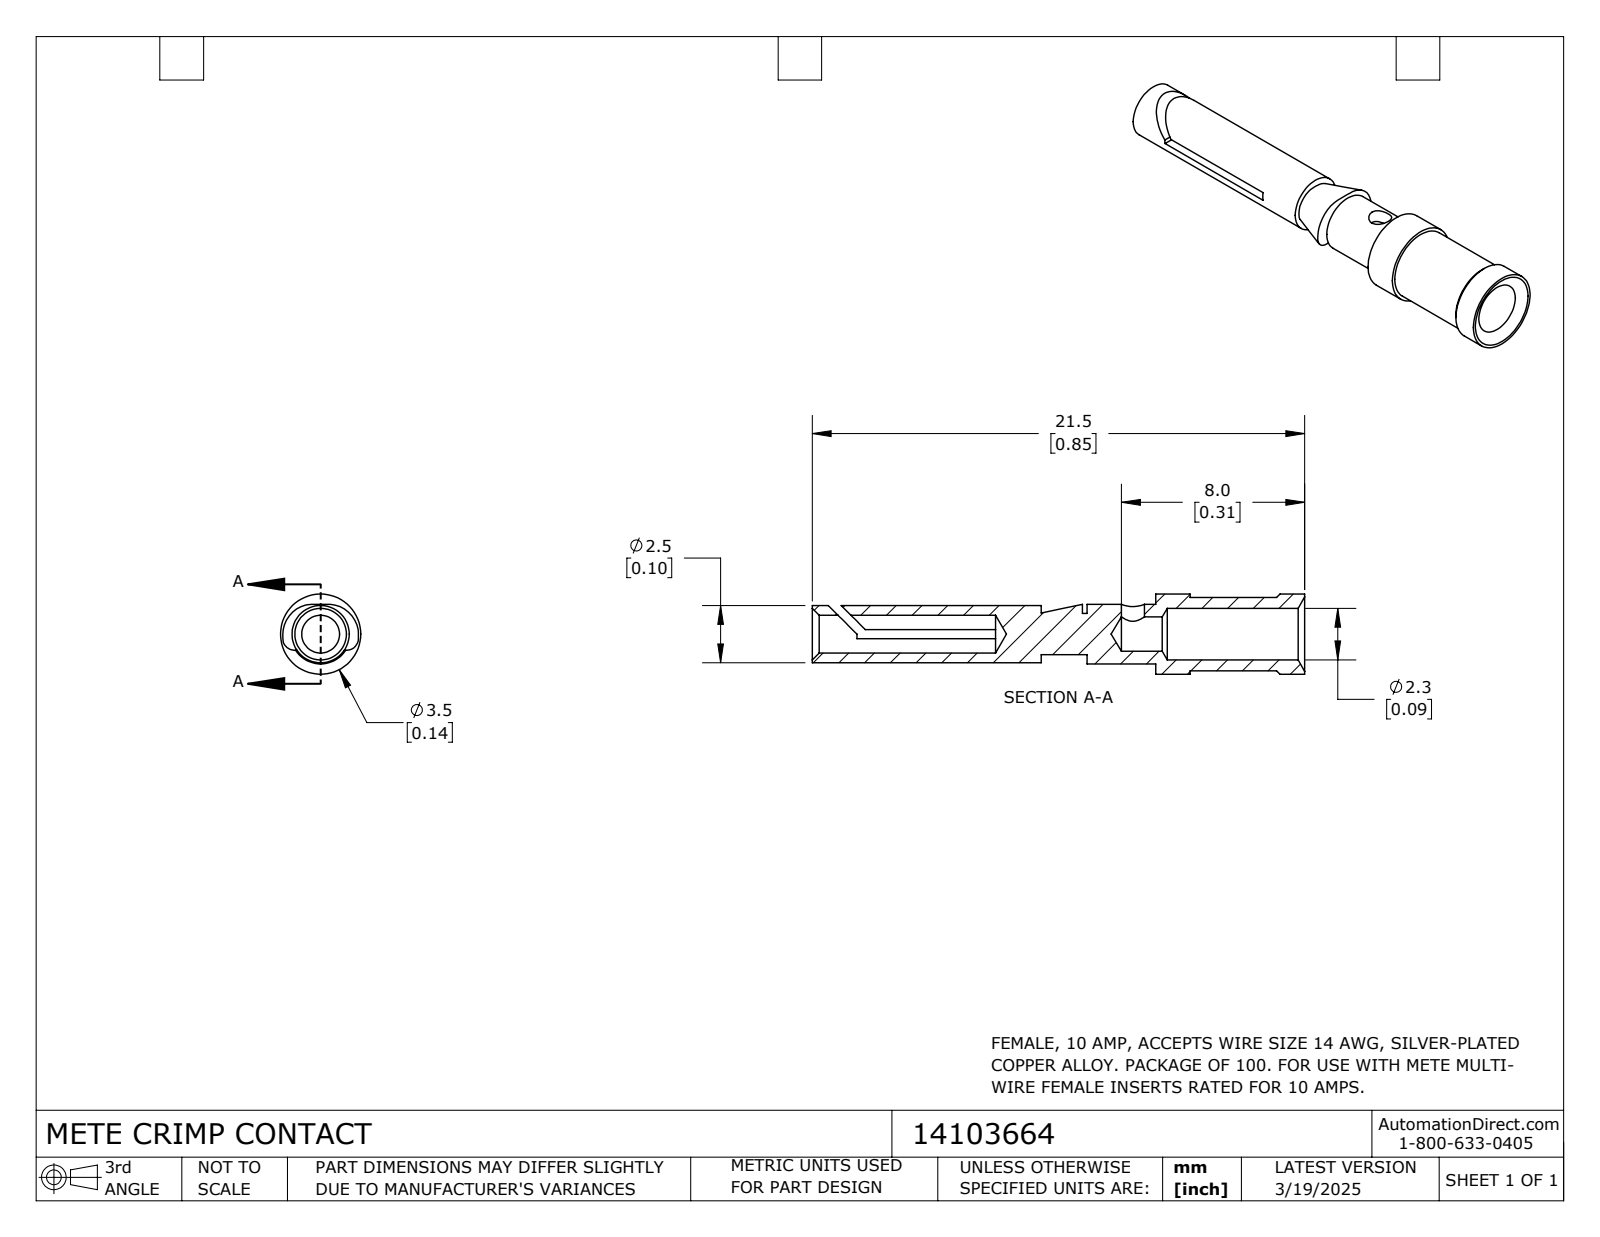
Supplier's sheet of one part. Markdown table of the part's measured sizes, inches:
| quantity | value |
| --- | --- |
| part name | 14103664 |
| STEP written by | SolidWorks 2024 (CONFIG_CONTROL_DESIGN) |
| units | inches |
| bodies | 1 solid, 52 faces (17 planar, 22 cylindrical, 13 other) |
| overall size | 0.846 × 0.138 × 0.138 |
| volume | 0.005 in³ |
| surface area | 0.477 in² |
| round holes (diameter × count) | 0.039 × 1, 0.059 × 1, 0.065 × 1, 0.089 × 1 |
| round bosses / shafts (diameter × count) | 0.138 × 1, 0.126 × 1, 0.102 × 1, 0.098 × 1, 0.071 × 1 |
| main face-to-face distances | 0.016, 0.126, 0.197, 0.256, 0.118, 0.079, 0.071, 0.059, 0.177, 0.185 |
